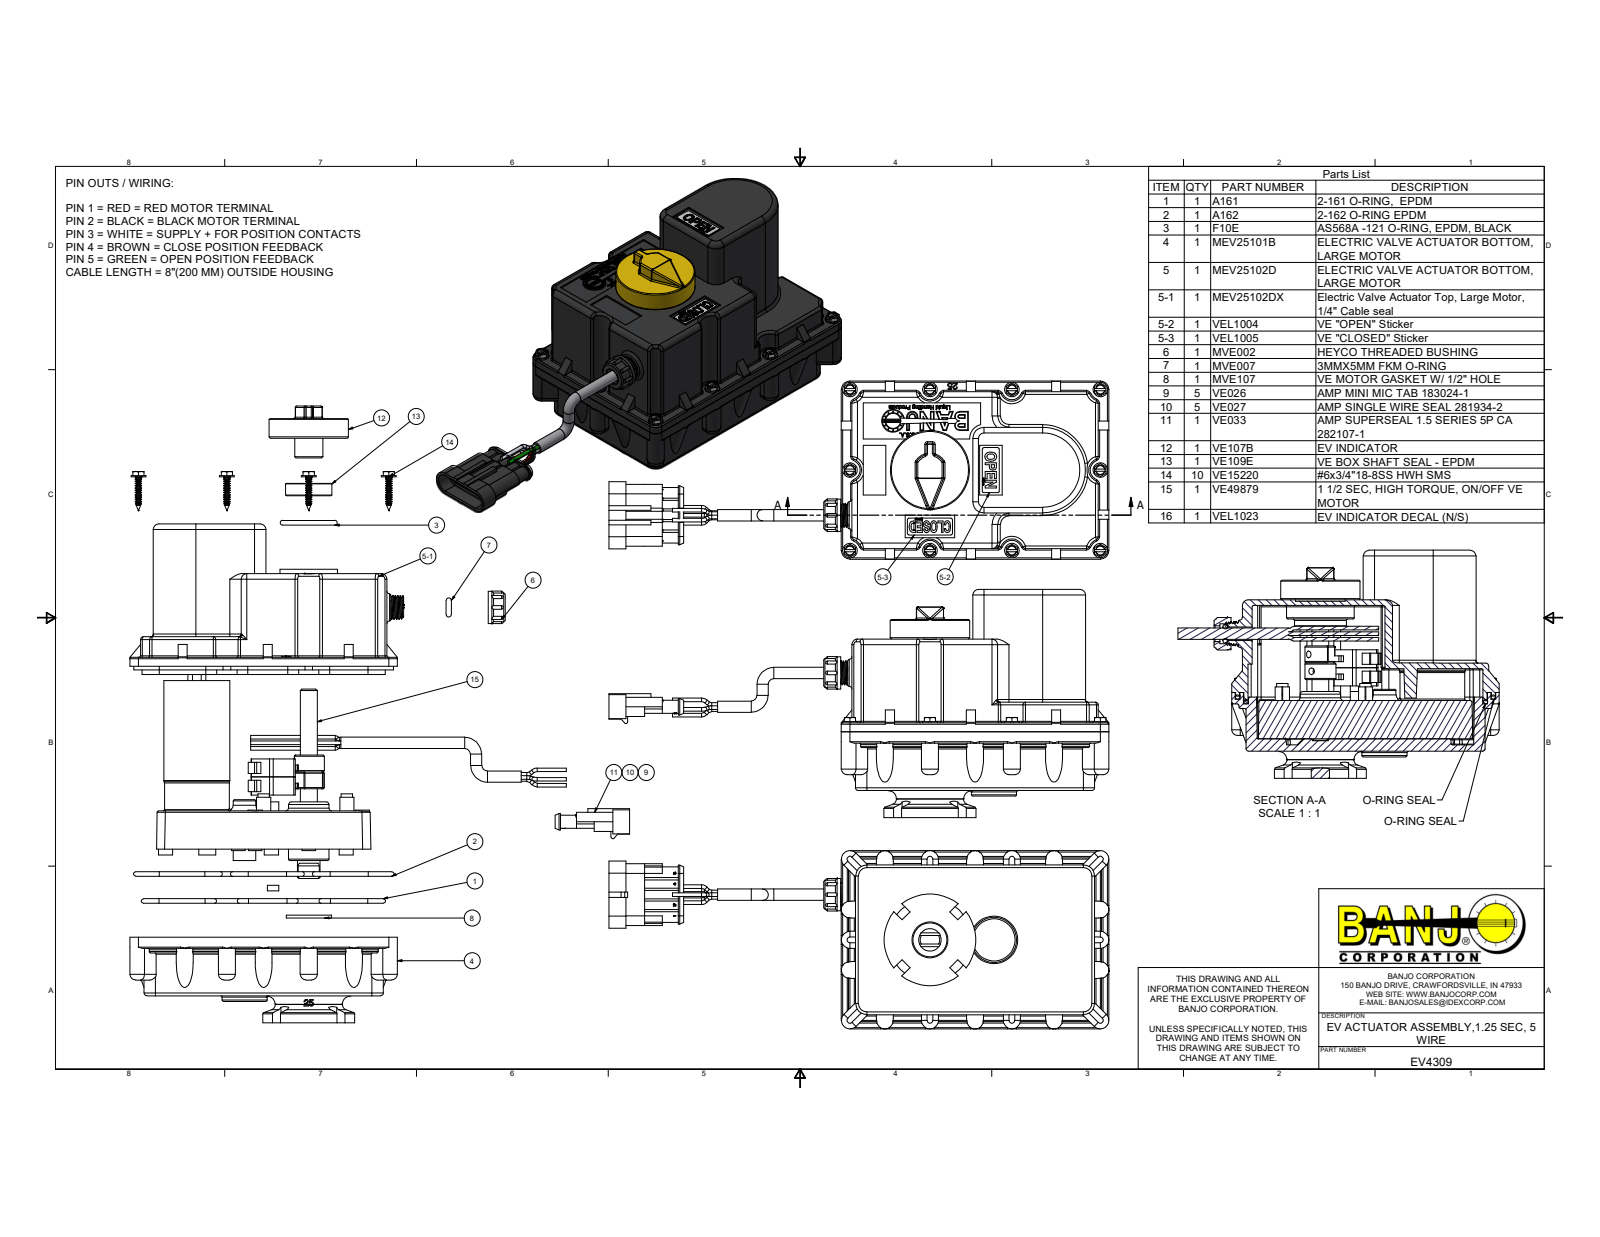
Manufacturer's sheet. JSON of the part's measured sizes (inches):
{"part_name": "EV4309; MEV25101B; MEV25102D; MEV25102DX (+8 more)", "step_written_by": "Autodesk Inventor 2022 (AUTOMOTIVE_DESIGN)", "units": "inches", "bodies": {"solids": 42, "faces": 4777, "planar": 2117, "cylindrical": 1227, "other": 1433}, "overall_size": [11.079, 5.055, 3.95], "volume_in3": 40.73, "surface_area_in2": 391.7, "round_holes": [[0.11, 10], [0.16, 10], [0.2, 10], [0.12, 6], [0.13, 6], [0.15, 6], [0.055, 5], [0.217, 5], [0.176, 4], [0.375, 3], [0.085, 2], [0.115, 2]], "round_bosses_or_shafts": [[0.08, 19], [0.328, 10], [0.138, 10], [0.25, 9], [0.103, 8], [0.315, 6], [0.3, 6], [0.232, 5]], "partial_cylinders_radius": [[0.03, 93], [0.06, 43], [0.02, 27], [0.125, 24], [0.315, 24], [0.5, 24], [0.02, 21], [0.007, 20]], "face_to_face_distances": [0.125, 3.355, 1.025, 3.23, 0.275, 0.79, 2.565, 0.045, 0.275, 2.955], "hole_center_spacings": [1.68, 2.058, 2.376, 1.785, 0.236, 0.348, 0.492, 1.188]}
